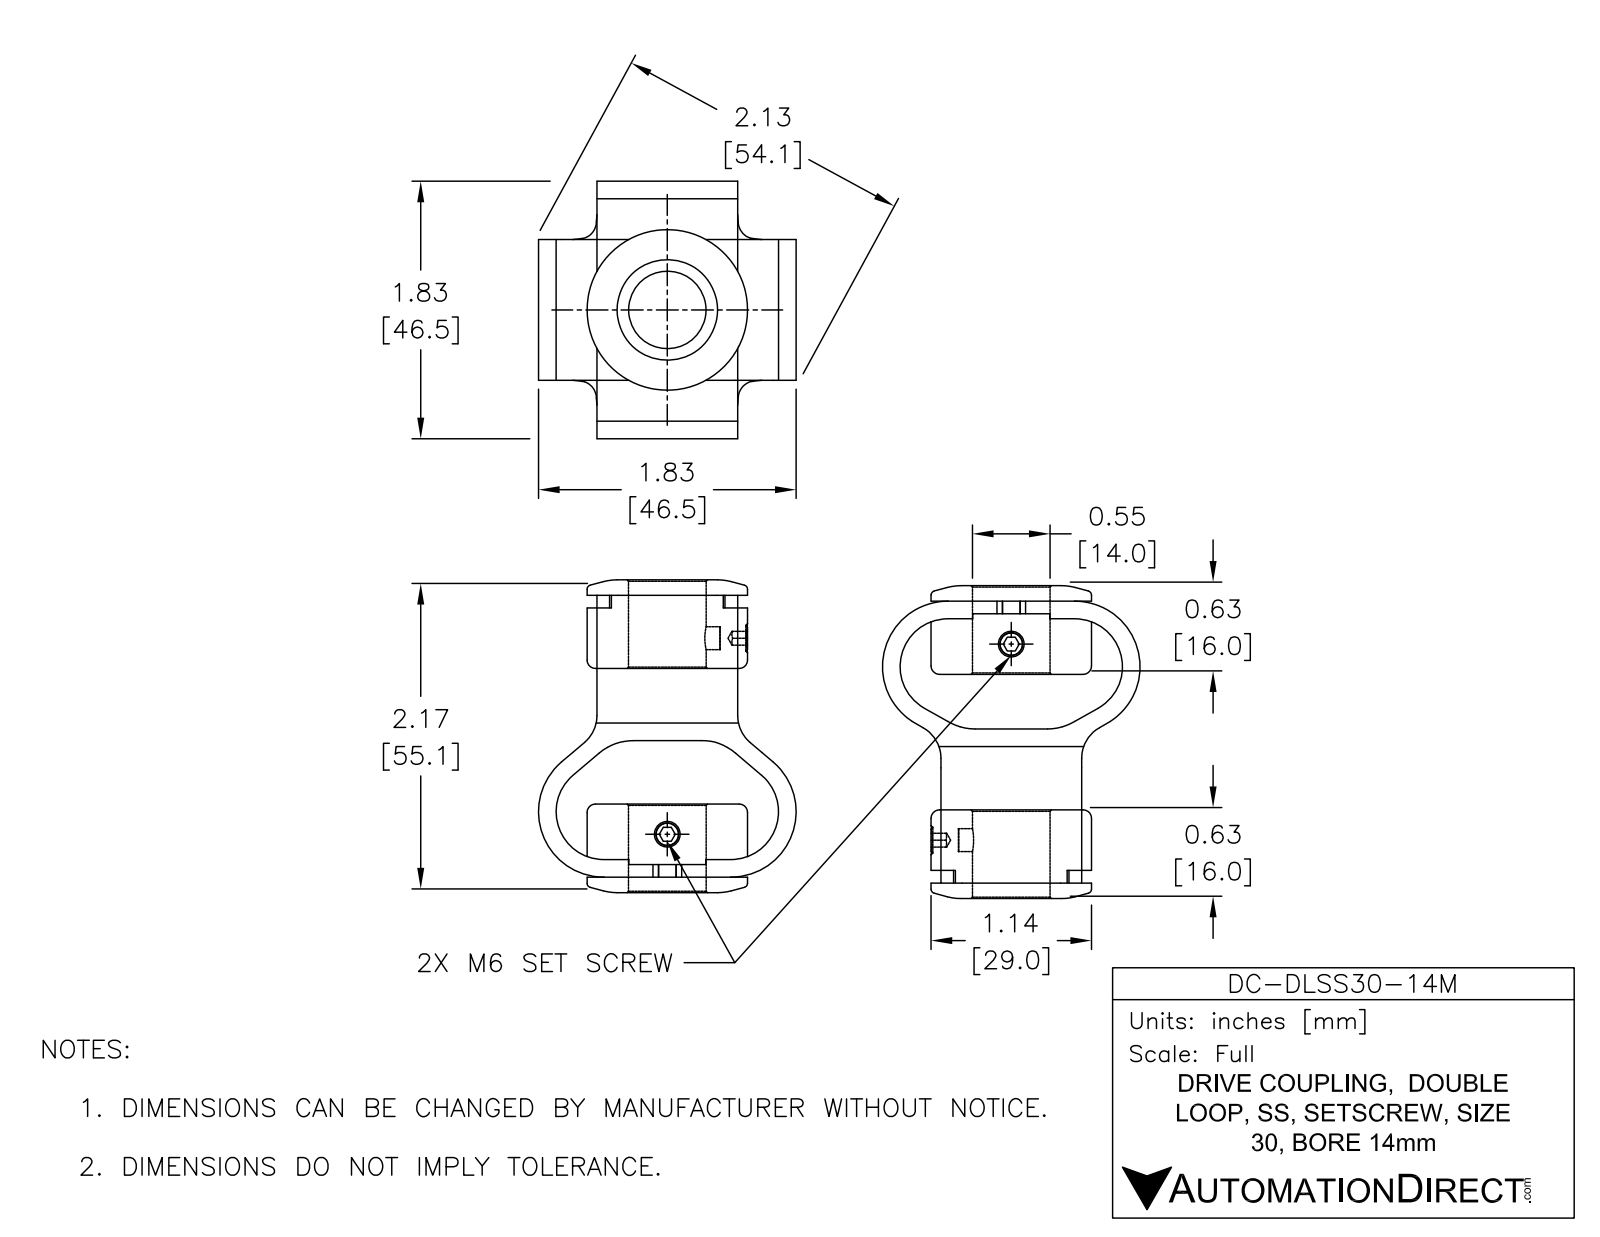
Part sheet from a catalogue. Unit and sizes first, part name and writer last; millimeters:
Units: millimetres
Overall size (bounding box): 56.46 × 46.48 × 46.48
Round holes (diameter × count): ⌀5.26 ×2, ⌀14 ×1
Round bosses / shafts (diameter × count): ⌀28.96 ×1
Partial cylindrical surfaces — rounded edges, fillets, slot ends (radius × count): R8.64 ×4, R9.53 ×4, R11.81 ×4, R10.41 ×1
Main face-to-face distances: 25.4, 24.46, 3.17, 14.61, 9.85, 11.44, 13.02, 24.64, 16, 40.46
Volume: 27 440 mm³ · Surface area: 15 050 mm²
Bodies: 1 solid, 165 faces (88 planar, 37 cylindrical, 40 other)
Part name (STEP PRODUCT): DC-DLSS30-14M
STEP written by: SolidWorks 2015 (AUTOMOTIVE_DESIGN)
